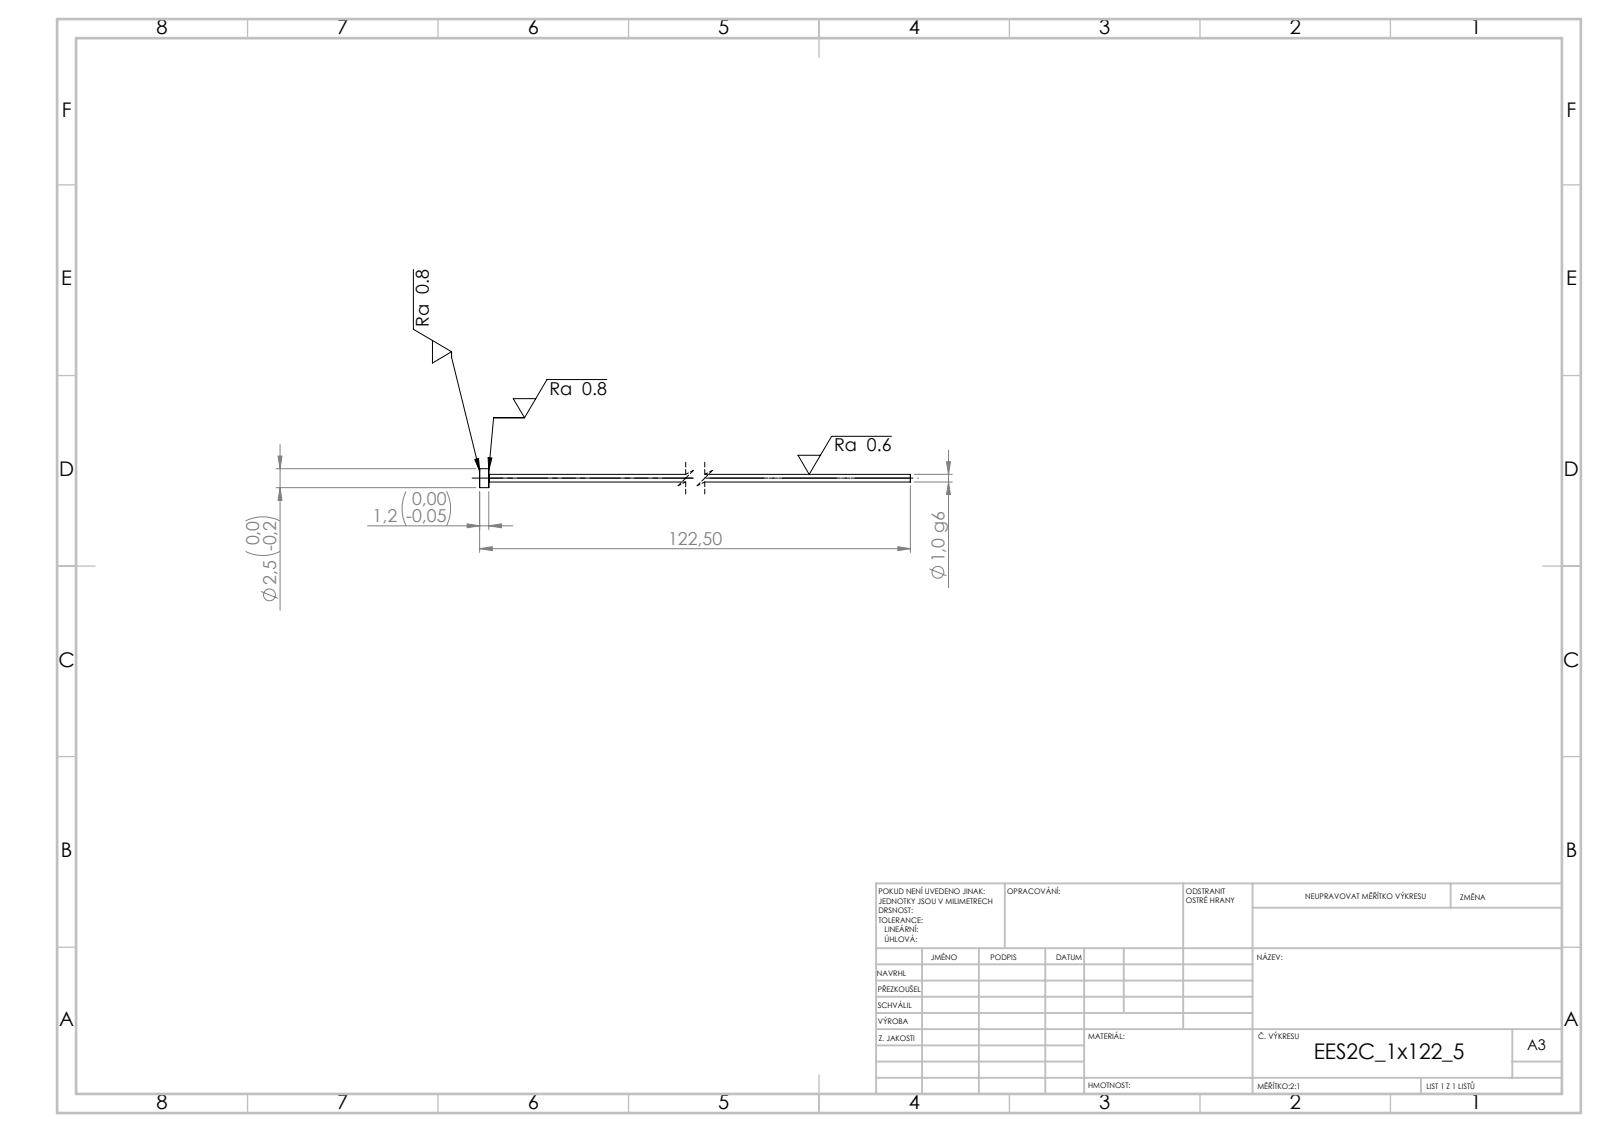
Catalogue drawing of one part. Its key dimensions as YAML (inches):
step_written_by: "SolidWorks 2019 (CONFIG_CONTROL_DESIGN)"
units: inches
bodies: {solids: 1, faces: 7, planar: 3, cylindrical: 4, other: 0}
overall_size: [4.823, 0.098, 0.098]
volume: 0.006
surface_area: 0.62
round_bosses_or_shafts:
  - {diameter: 0.098, count: 1}
  - {diameter: 0.039, count: 1}
face_to_face_distances: [0.047, 4.823, 4.776]
